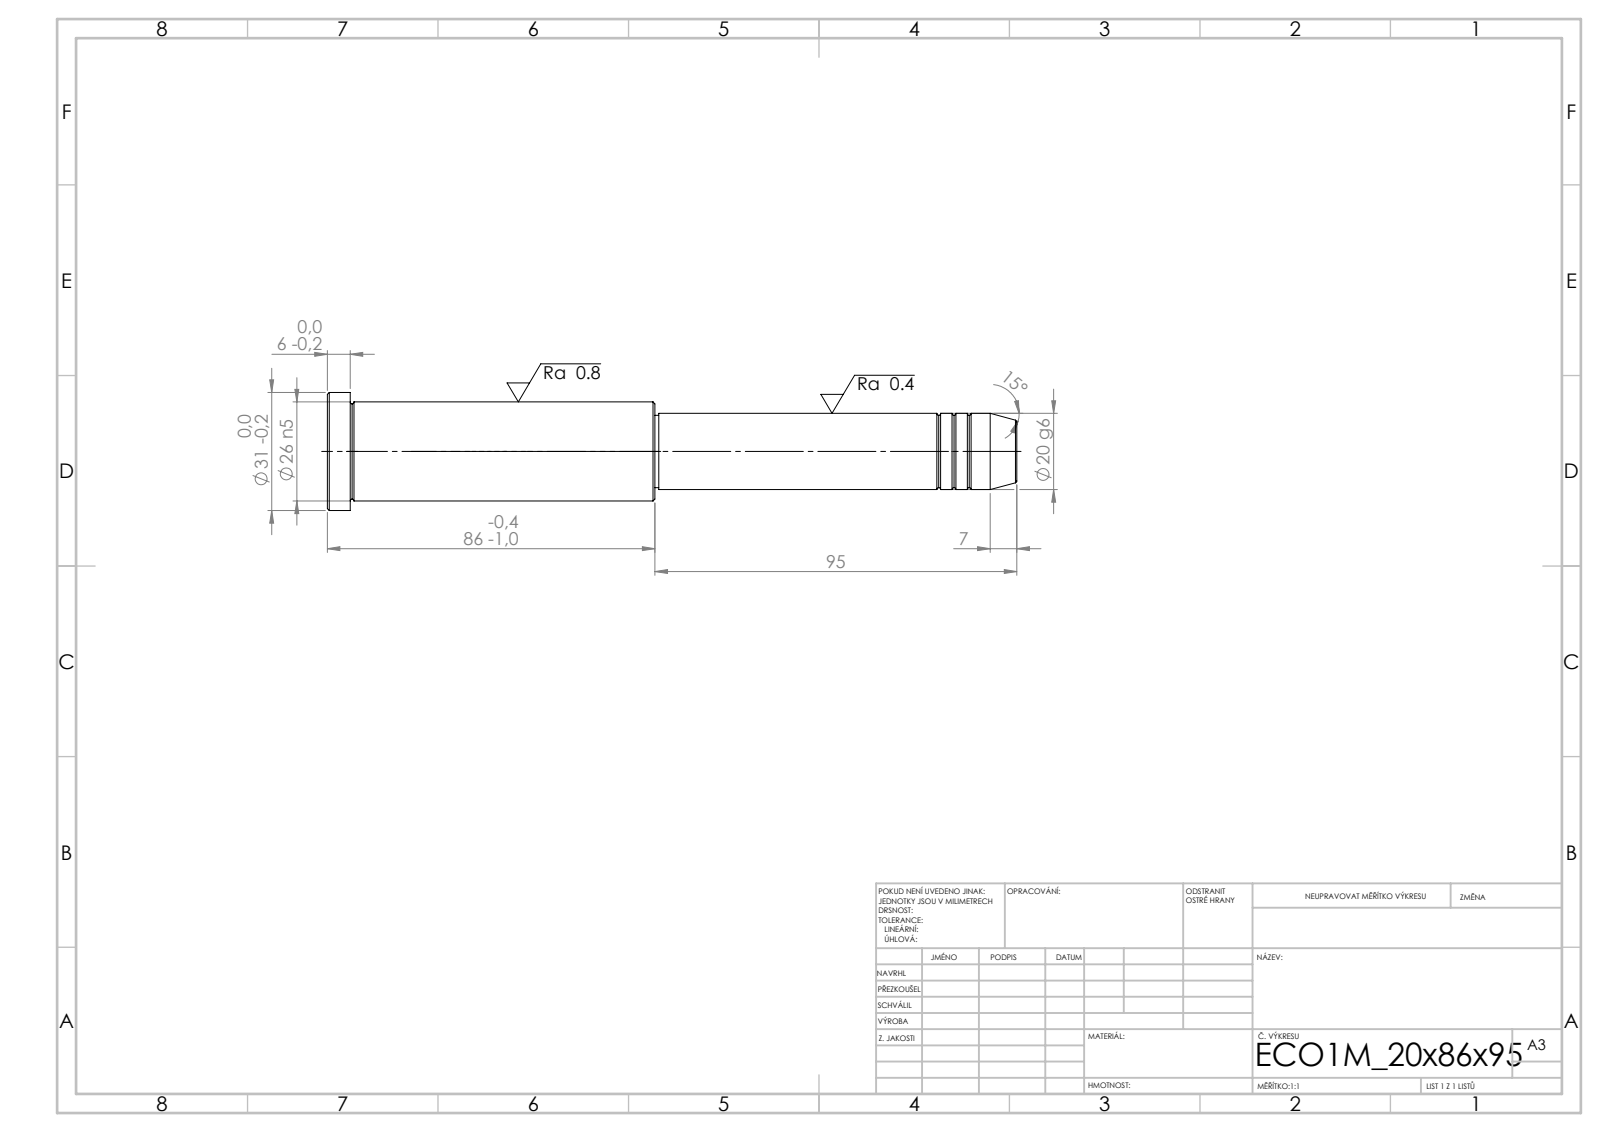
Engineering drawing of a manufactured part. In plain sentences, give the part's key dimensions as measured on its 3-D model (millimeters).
Its 3-D file was written by "SolidWorks 2019 (CONFIG_CONTROL_DESIGN)". It is 1 solid with 43 faces: 5 planar, 14 cylindrical and 24 other. Overall it measures 181 by 31 by 31 millimeters. Its volume is 76 303 cubic millimeters and its surface area 14 604 square millimeters. Round bosses or shafts: 1 of diameter 31, 1 of diameter 26, 1 of diameter 20, 1 of diameter 19. The main face-to-face distances are 6, 80, 86, 95, 175, 181, 94, 1, 81, 87.
